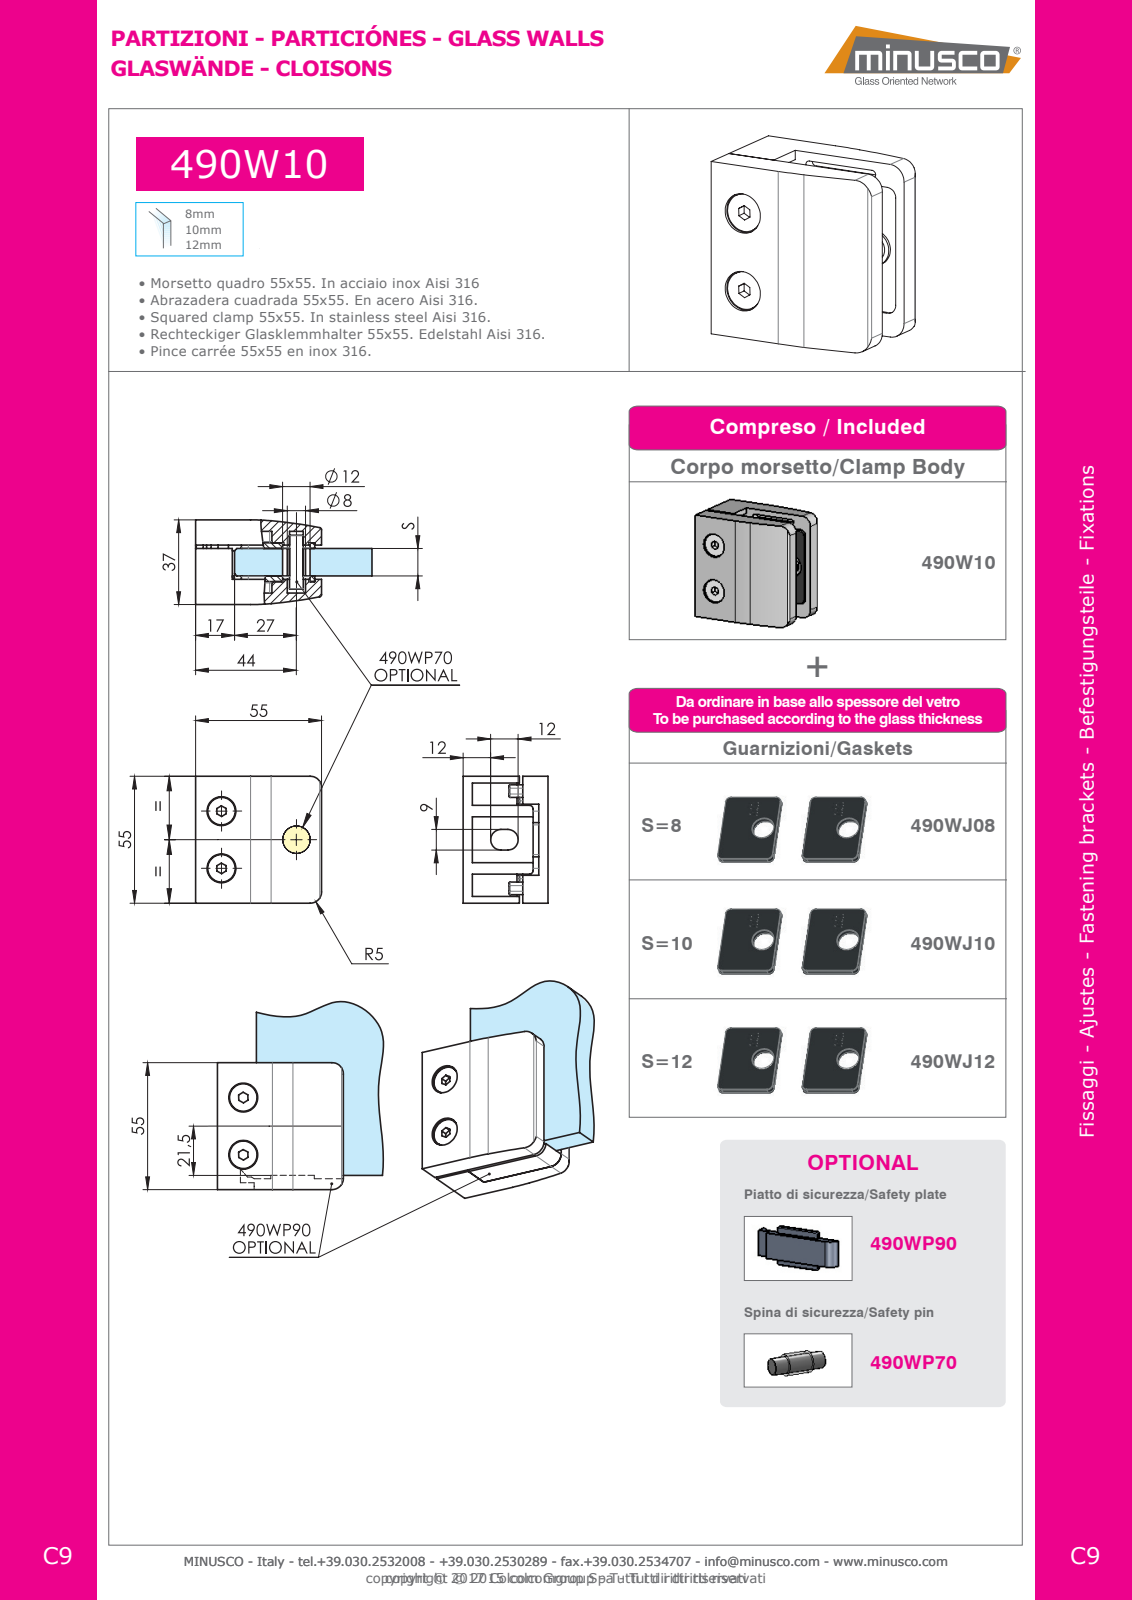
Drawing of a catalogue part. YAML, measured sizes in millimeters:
step_written_by: "Spatial InterOp 3D (CONFIG_CONTROL_DESIGN)"
units: millimeters
bodies: {solids: 12, faces: 954, planar: 338, cylindrical: 336, other: 280}
overall_size: [55.5, 55, 37]
volume: 69782
surface_area: 36172
round_holes:
  - {diameter: 5, count: 2}
  - {diameter: 6.6, count: 2}
  - {diameter: 12.6, count: 2}
  - {diameter: 6, count: 1}
  - {diameter: 8, count: 1}
  - {diameter: 12, count: 1}
round_bosses_or_shafts:
  - {diameter: 12, count: 2}
  - {diameter: 6, count: 2}
  - {diameter: 11, count: 1}
partial_cylinders:
  - {radius: 0.3, count: 88}
  - {radius: 0.5, count: 32}
  - {radius: 1, count: 21}
  - {radius: 1.5, count: 16}
  - {radius: 3, count: 8}
  - {radius: 1.25, count: 4}
  - {radius: 2, count: 4}
  - {radius: 4.5, count: 2}
face_to_face_distances: [13.5, 10, 1, 3.5, 2.5, 16, 23.5, 12.5, 26, 27]
hole_center_spacings: [35.01, 25]
